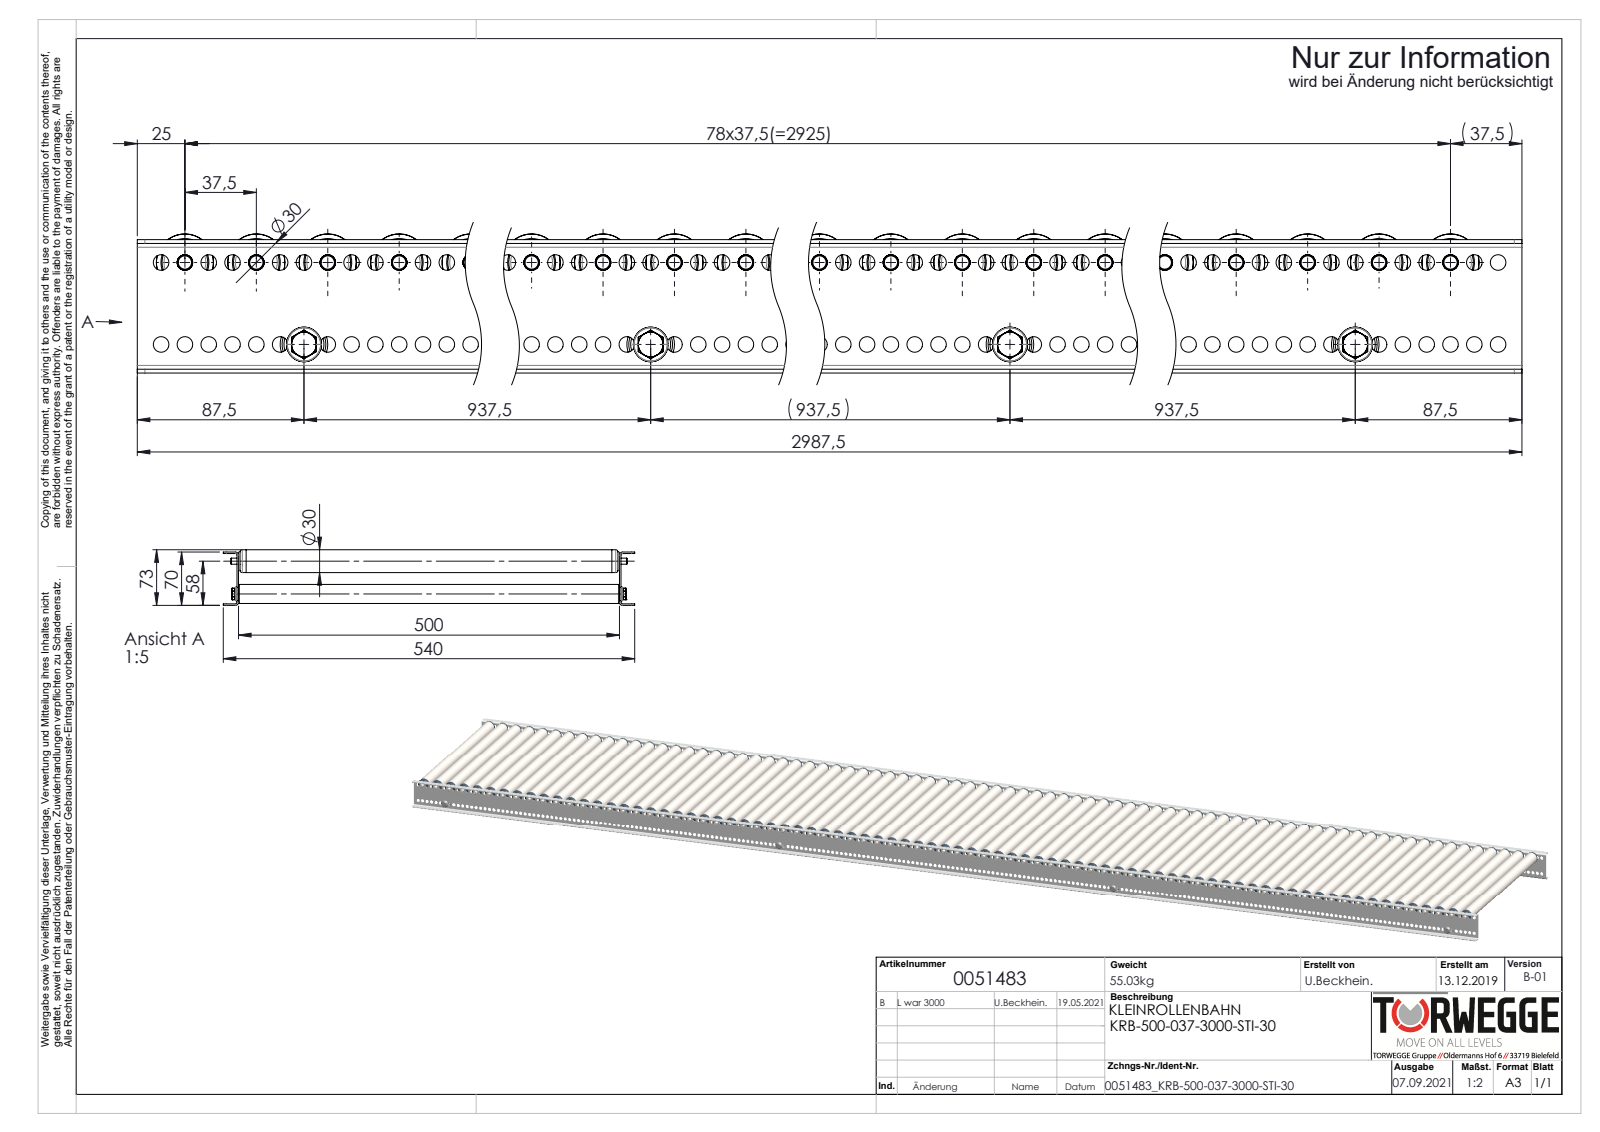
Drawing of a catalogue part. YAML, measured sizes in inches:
part_name: "0051483; Traversen_KFG_L500; S100994_Sperrzahnschraube_M08x16-8.8-A2K; 0039778-Achse-ST-Ø08-KFG_AL520-G-FA (+6 more)"
step_written_by: "SolidWorks 2020 (AUTOMOTIVE_DESIGN)"
units: inches
bodies: {solids: 496, faces: 20898, planar: 6524, cylindrical: 8320, other: 6054}
overall_size: [117.618, 21.26, 2.874]
volume: 530.1
surface_area: 16260
round_holes:
  - {diameter: 0.323, count: 476}
  - {diameter: 0.315, count: 79}
  - {diameter: 0.319, count: 79}
  - {diameter: 0.913, count: 79}
  - {diameter: 0.992, count: 79}
  - {diameter: 1.063, count: 79}
  - {diameter: 0.268, count: 4}
  - {diameter: 0.827, count: 4}
round_bosses_or_shafts:
  - {diameter: 1.181, count: 79}
  - {diameter: 1.177, count: 79}
  - {diameter: 1.067, count: 79}
  - {diameter: 1.055, count: 79}
  - {diameter: 0.945, count: 79}
  - {diameter: 0.551, count: 79}
  - {diameter: 0.984, count: 4}
  - {diameter: 0.315, count: 4}
partial_cylinders:
  - {radius: 0.199, count: 79}
  - {radius: 0.157, count: 8}
  - {radius: 0.079, count: 4}
face_to_face_distances: [0.079, 19.764, 19.685, 2.677, 19.843, 2.756, 2.598, 0.394, 19.291, 0.787]
hole_center_spacings: [0.492, 0.984, 1.476, 1.969, 2.461, 2.953, 3.445, 3.937]
